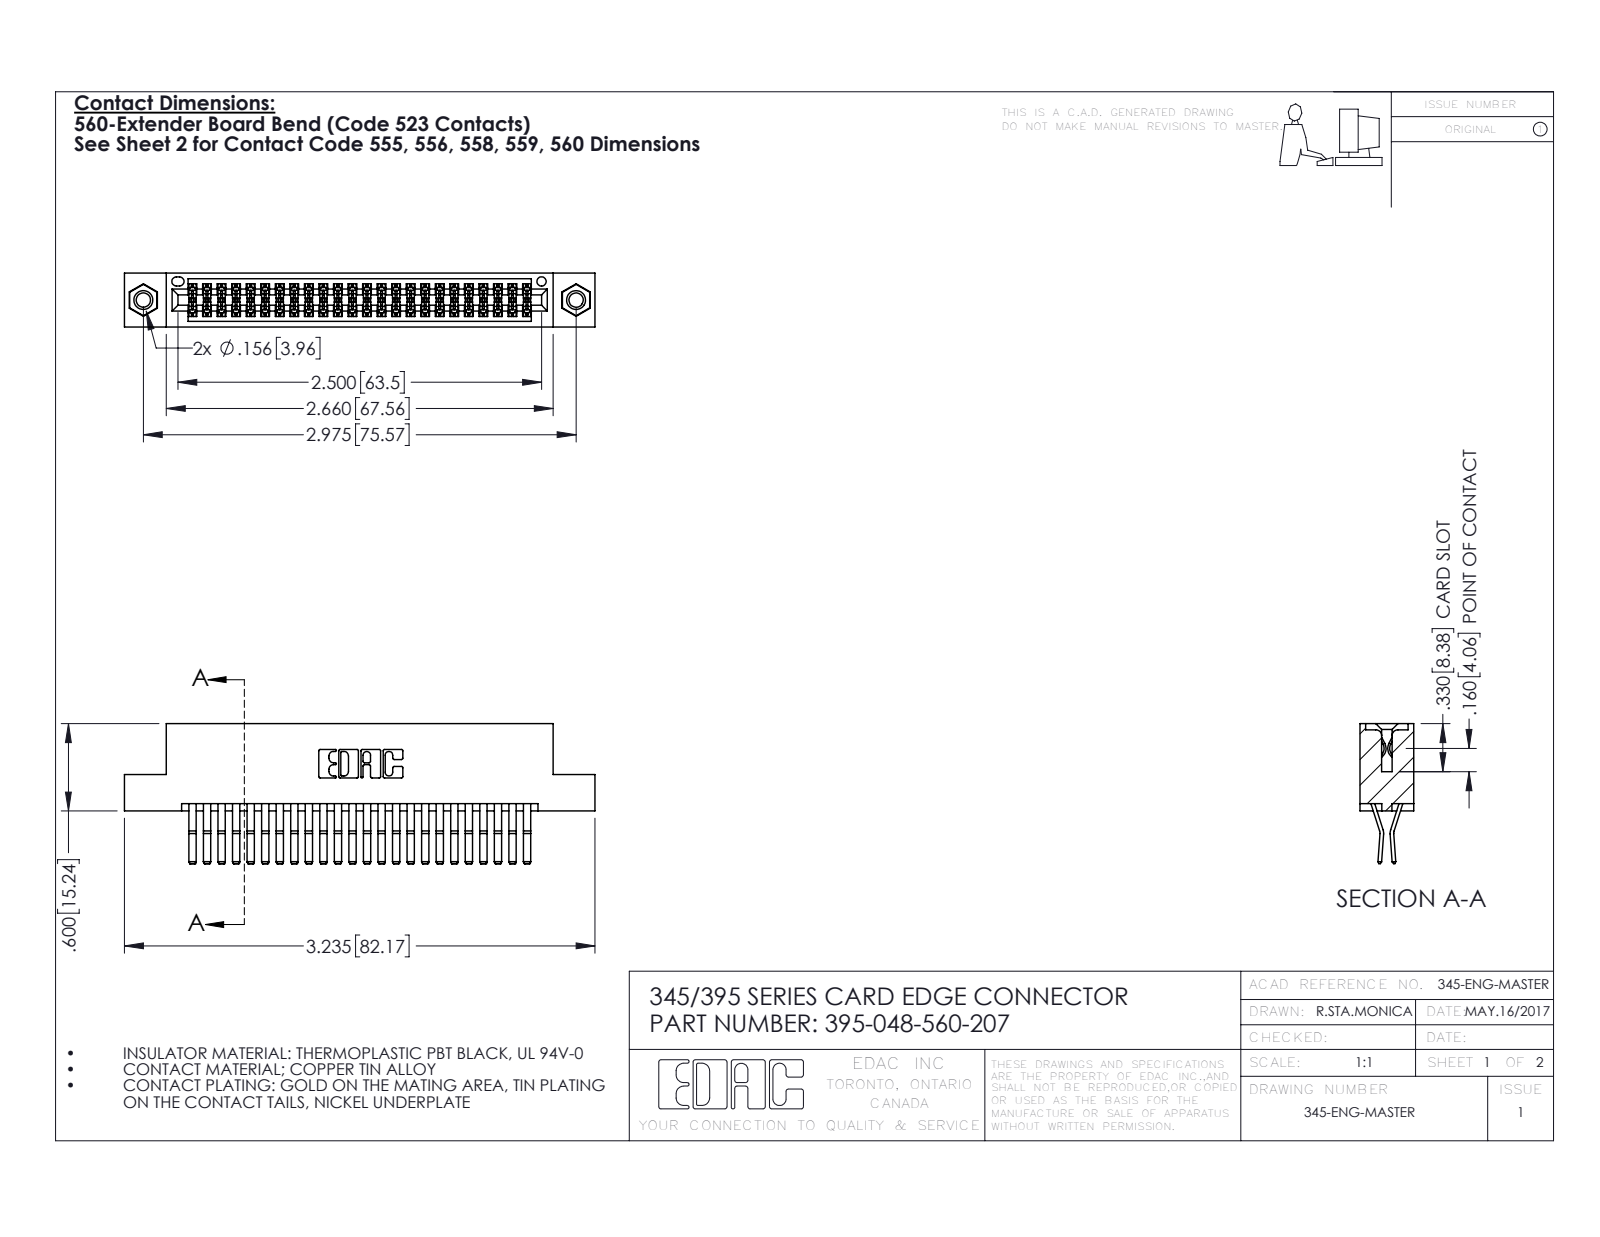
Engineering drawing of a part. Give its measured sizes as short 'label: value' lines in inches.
name: 345-292-001_560 Tail; 395-048-560-207; 345-250-001_345-250-005-103; 345 Part_Flush Mounting Lugs - 0.156 Dia-TI
written by: SolidWorks 2016 (CONFIG_CONTROL_DESIGN)
unit: in
bodies: 51 solids, 2682 faces (1696 planar, 970 cylindrical, 16 other)
size: 3.235 × 0.962 × 0.37
volume: 0.495 in³; area: 19.35 in²
holes: 2× ⌀0.098, 2× ⌀0.125, 2× ⌀0.156, 1× ⌀0.064
bosses: 2× ⌀0.155
rounds: 72× R0.006, 22× R0.01, 6× R0.007, 6× R0.031, 3× R0.026, 2× R0.01, 2× R0.014, 2× R0.019
face distances: 0.025, 0.072, 0.298, 0.2, 0.37, 0.098, 0.272, 0.225, 0.175, 0.149
hole spacings: 0.27, 2.741, 2.975
